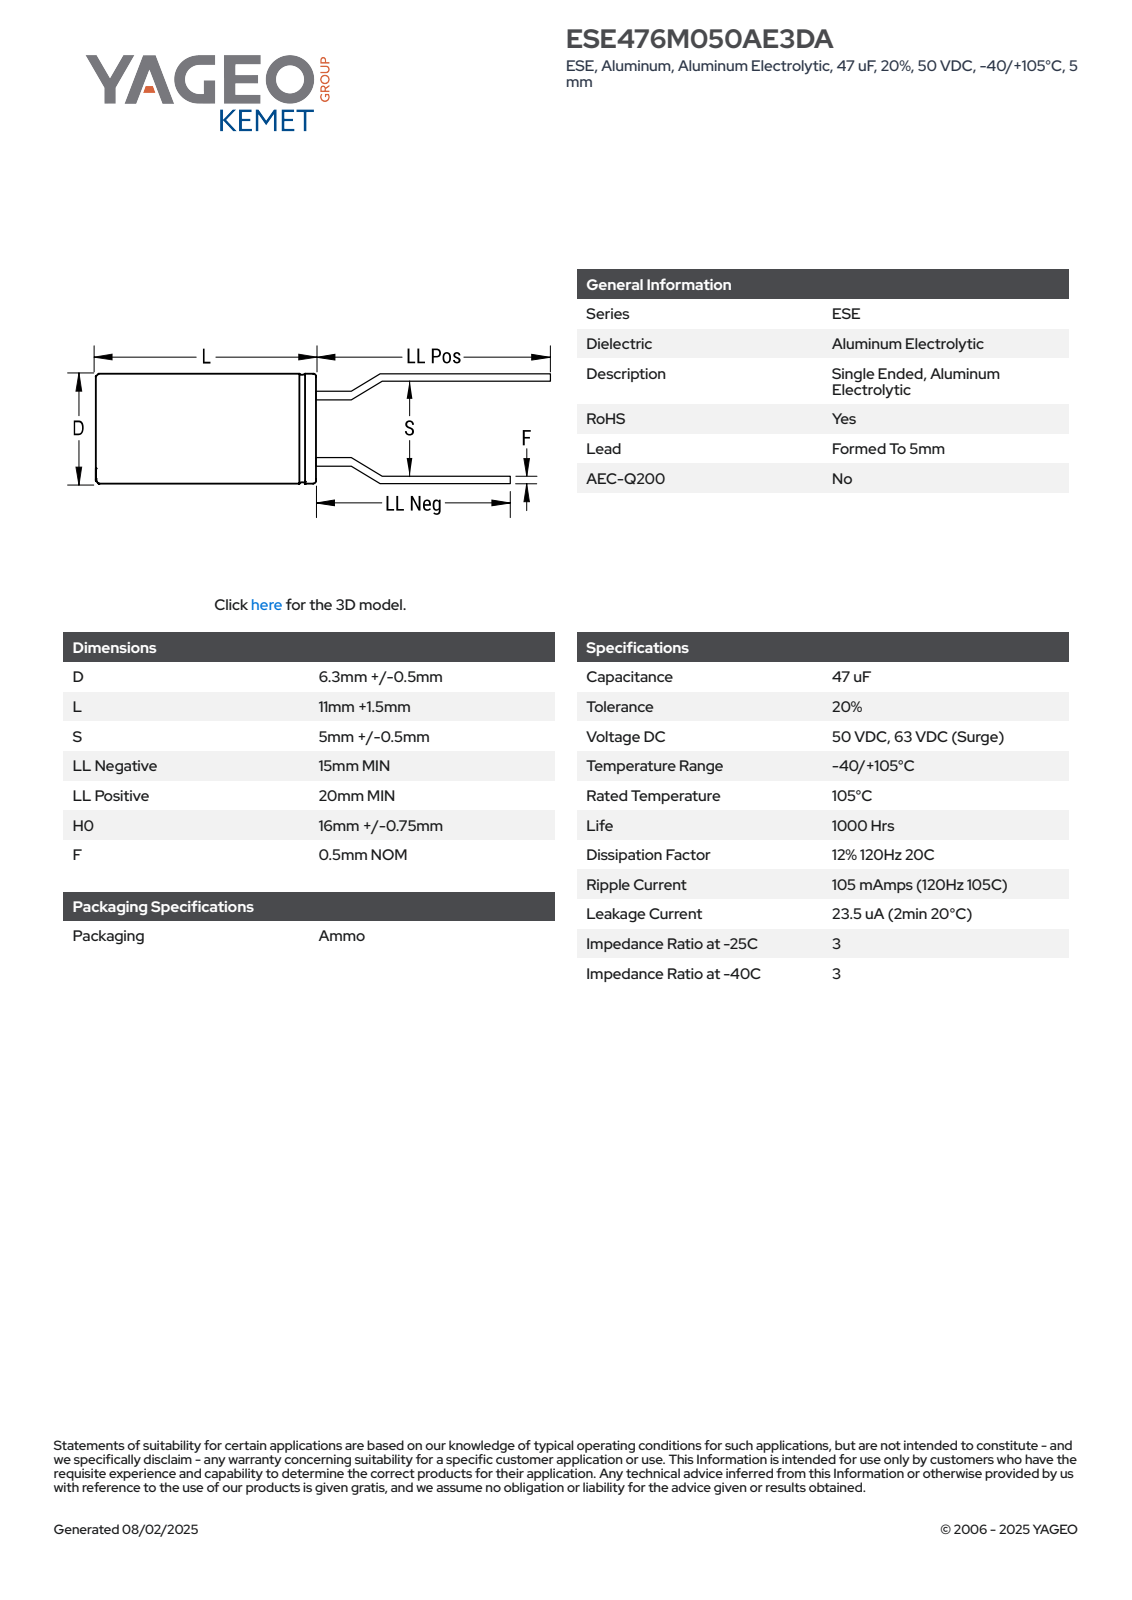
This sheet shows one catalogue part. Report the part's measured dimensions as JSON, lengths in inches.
{"part_name": "CAR_KTRF5_6.3X11_D6.8L12.5S5F0.5", "step_written_by": "SolidWorks 2014 (AUTOMOTIVE_DESIGN)", "units": "inches", "bodies": {"solids": 4, "faces": 81, "planar": 61, "cylindrical": 16, "other": 4}, "overall_size": [0.984, 0.268, 0.268], "volume_in3": 0.028, "surface_area_in2": 0.608, "round_bosses_or_shafts": [[0.02, 6], [0.268, 1]], "face_to_face_distances": [0.492, 0.493, 0.985, 0.984, 0.032, 0.014, 0.13, 0.02, 0.066, 0.139]}
